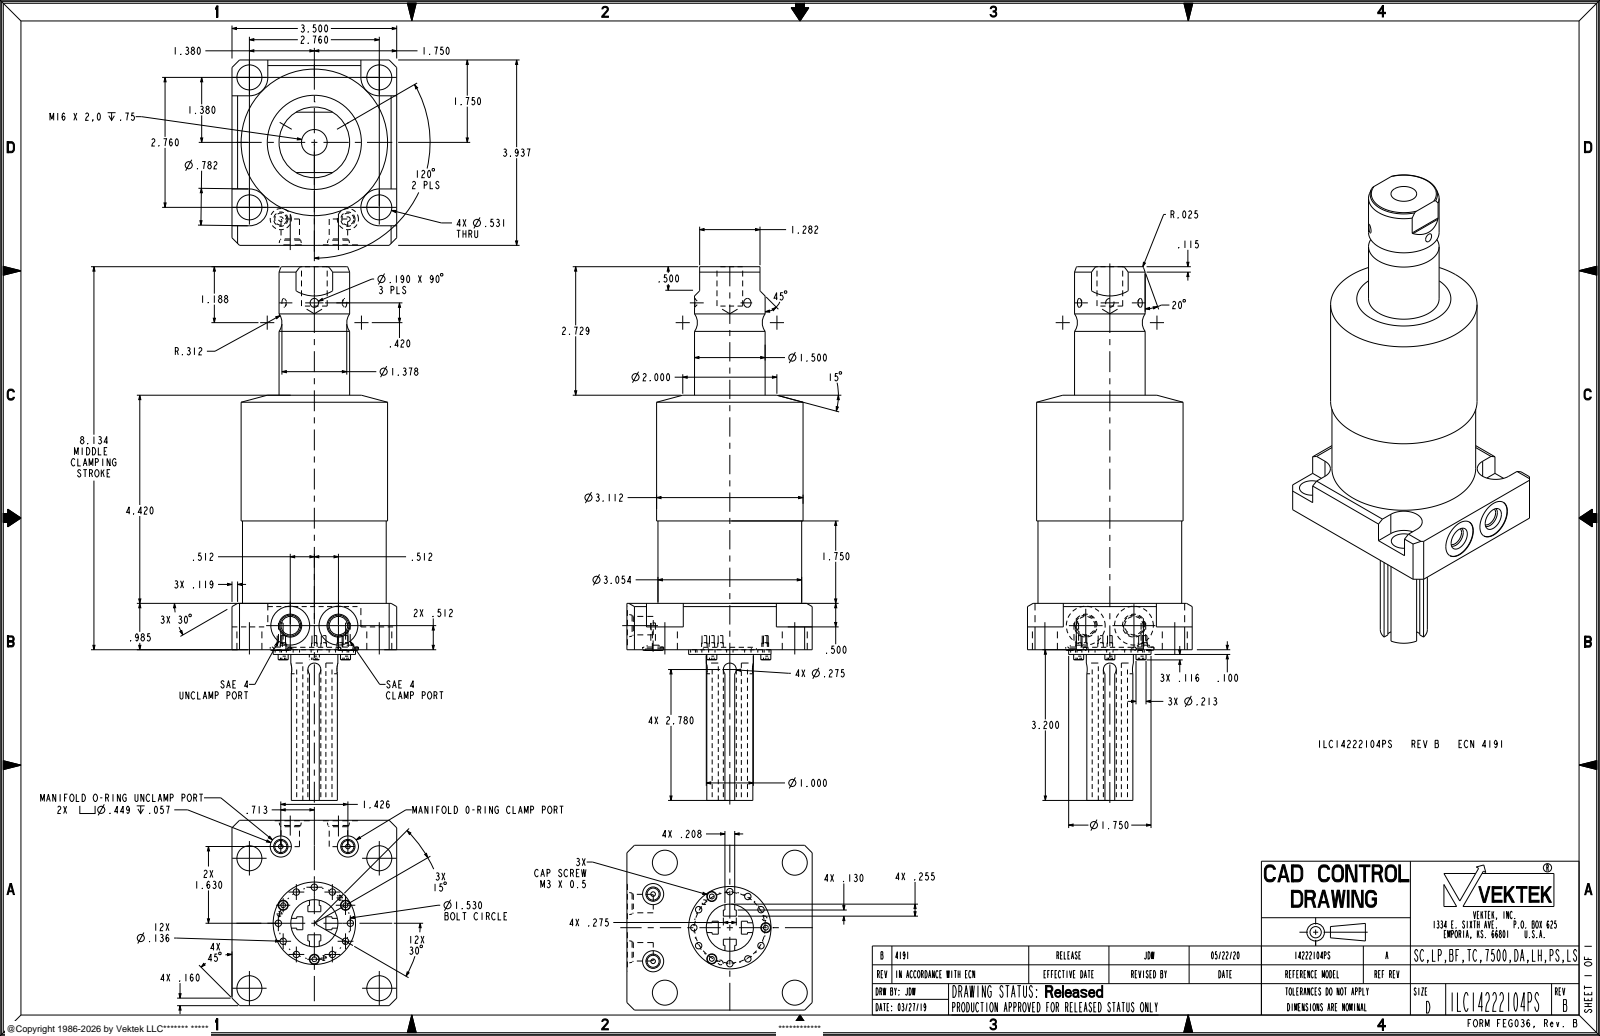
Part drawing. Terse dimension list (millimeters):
name: ILC14222104PS
written by: PRO/ENGINEER BY PARAMETRIC TECHNOLOGY CORPORATION, 2013320 (AUTOMOTIVE_DESIGN)
unit: mm
bodies: 1 solid, 280 faces (130 planar, 112 cylindrical, 38 other)
size: 287.9 × 100 × 88.9
volume: 835 700 mm³; area: 79 230 mm²
holes: 12× ⌀3.5, 6× ⌀2.5, 4× ⌀13.5, 2× ⌀2.5, 2× ⌀6.5, 2× ⌀10, 2× ⌀11.4, 2× ⌀21, 1× ⌀13.9, 1× ⌀28.7
bosses: 6× ⌀3, 3× ⌀5.4, 1× ⌀79, 1× ⌀77.6, 1× ⌀44.5, 1× ⌀38.1, 1× ⌀25.4, 1× ⌀23.3
rounds: 4× R9.9, 2× R0.8, 2× R3.5
face distances: 25, 2.7, 9.7, 88.9, 3.6, 8.9, 0.8, 6.1, 50.7, 38.2
hole spacings: 19.4, 33.7, 10.1, 19.4, 27.5, 31.2, 37.5, 38.4
